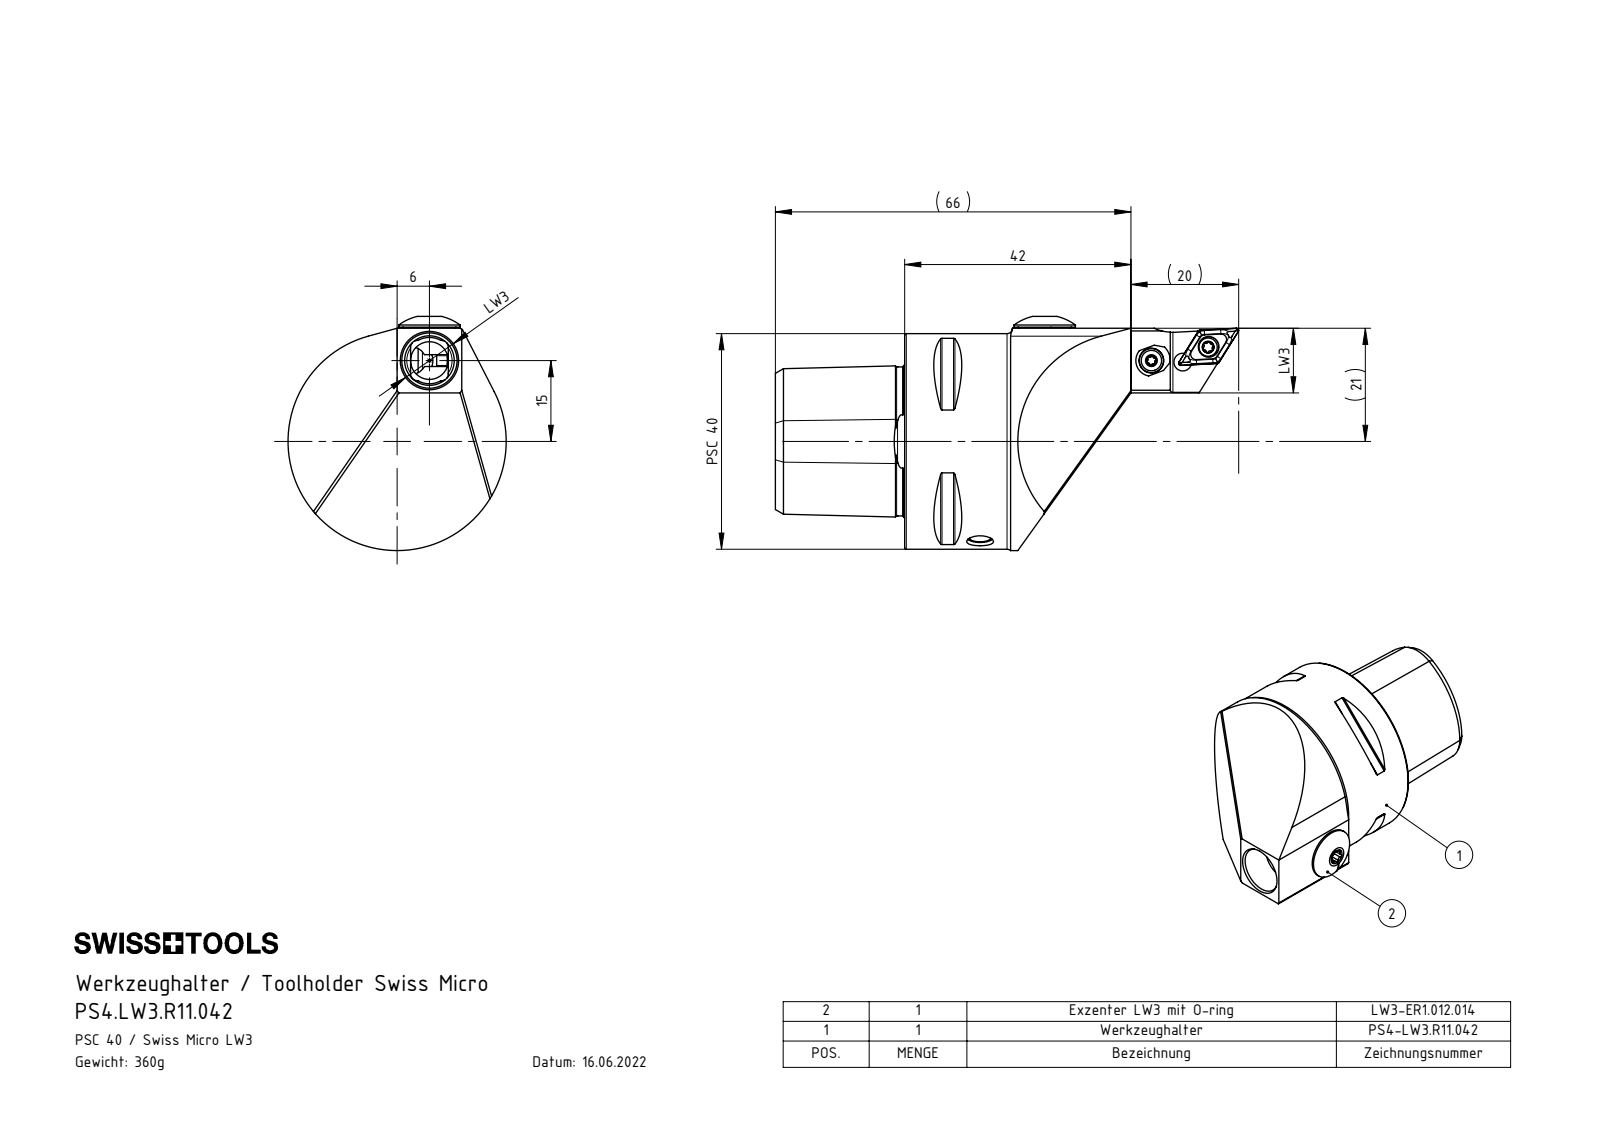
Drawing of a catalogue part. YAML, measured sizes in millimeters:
part_name: "LW3-ER1.012.014_C_Standard<Wie bearbeitet>; PS4.LW3.R11.042; LW3-ER1.012.014; KVT_MB_600_050 (+2 more)"
step_written_by: "SolidWorks 2017 (AUTOMOTIVE_DESIGN)"
units: millimeters
bodies: {solids: 6, faces: 223, planar: 66, cylindrical: 65, other: 92}
overall_size: [66, 43.25, 40.5]
volume: 45952
surface_area: 12845
round_holes:
  - {diameter: 4, count: 2}
  - {diameter: 4.2, count: 2}
  - {diameter: 1, count: 1}
  - {diameter: 2.4, count: 1}
  - {diameter: 4.6, count: 1}
  - {diameter: 5, count: 1}
  - {diameter: 7, count: 1}
  - {diameter: 9.21, count: 1}
  - {diameter: 12.5, count: 1}
  - {diameter: 18, count: 1}
  - {diameter: 20, count: 1}
round_bosses_or_shafts:
  - {diameter: 40, count: 1}
  - {diameter: 11.4, count: 1}
  - {diameter: 9.5, count: 1}
  - {diameter: 7.7, count: 1}
  - {diameter: 5, count: 1}
partial_cylinders:
  - {radius: 0.3, count: 8}
  - {radius: 0.34, count: 6}
  - {radius: 0.59, count: 6}
  - {radius: 1.3, count: 4}
  - {radius: 2.5, count: 2}
  - {radius: 3, count: 1}
  - {radius: 3.6, count: 1}
  - {radius: 3.7, count: 1}
face_to_face_distances: [24, 15.52, 35.3, 1.1, 12, 15, 9, 66, 51, 42]
hole_center_spacings: [16.16, 23.5]
